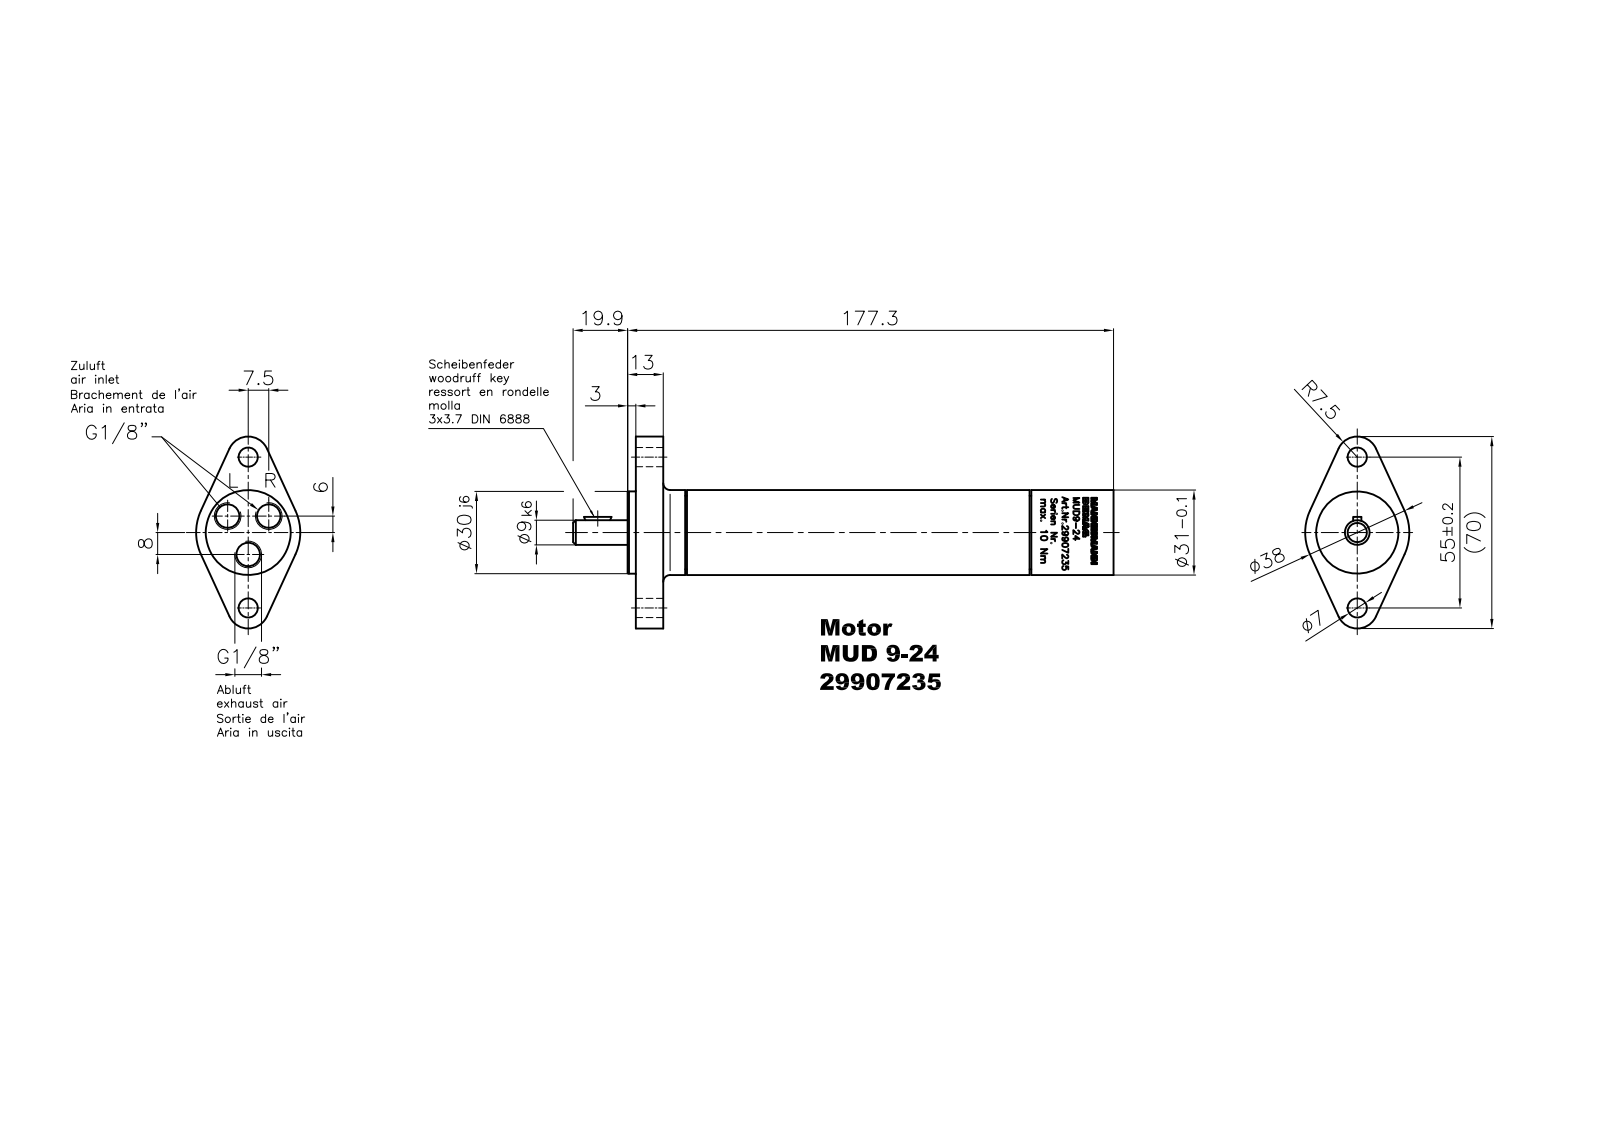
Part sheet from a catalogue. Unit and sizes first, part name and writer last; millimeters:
Units: millimetres
Overall size (bounding box): 197.3 × 70 × 38
Round holes (diameter × count): ⌀28 ×1
Round bosses / shafts (diameter × count): ⌀31 ×1, ⌀30 ×1, ⌀26.79 ×1, ⌀9 ×1
Partial cylindrical surfaces — rounded edges, fillets, slot ends (radius × count): R4 ×3, R7.5 ×2, R5 ×1, R5.25 ×1, R12 ×1, R19 ×1
Main face-to-face distances: 10, 3, 13, 177.3, 174.3, 164.3, 37.98, 0.65, 125.65, 162.95
Volume: 141 413 mm³ · Surface area: 24 896 mm²
Bodies: 1 solid, 64 faces (27 planar, 20 cylindrical, 17 other)
Part name (STEP PRODUCT): MUD 9-24_29907235
STEP written by: Autodesk Inventor 2008 (CONFIG_CONTROL_DESIGN)
